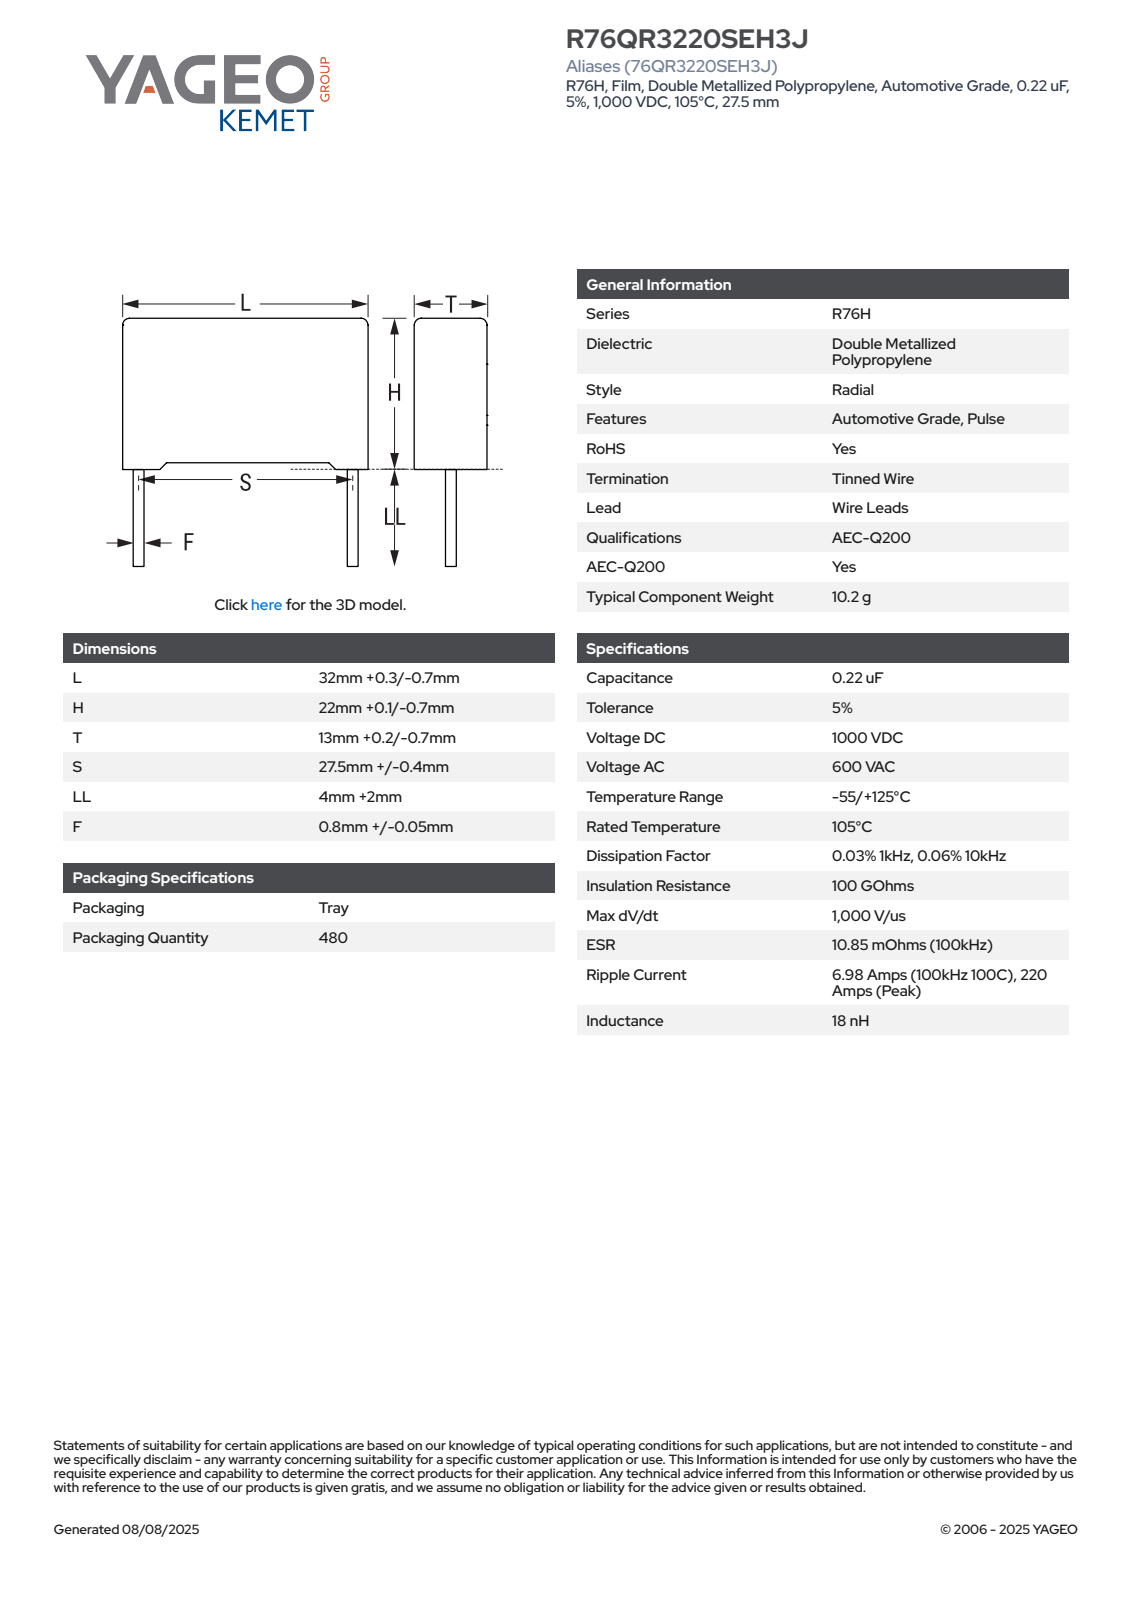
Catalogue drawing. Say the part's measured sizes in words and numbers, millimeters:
The part is named "CFR_RB2R76_32X22X13_L32.3H22.1T13.2S27.5LL6F0.85". Its 3-D file was written by "SolidWorks 2014 (AUTOMOTIVE_DESIGN)". It is 4 solids with 85 faces: 77 planar, 8 cylindrical and 0 other. Overall it measures 32.3 by 28.1 by 13.21 millimeters. Its volume is 9 134 cubic millimeters and its surface area 2 950 square millimeters. Round bosses or shafts: 2 of diameter 0.85. Partial cylindrical surfaces (rounded edges, fillets, slot ends): 4 of radius 0.5. The main face-to-face distances are 13.2, 21.34, 32.3, 21.35, 0.75, 0.76, 22.1, 1.08, 13.21, 31.22.
